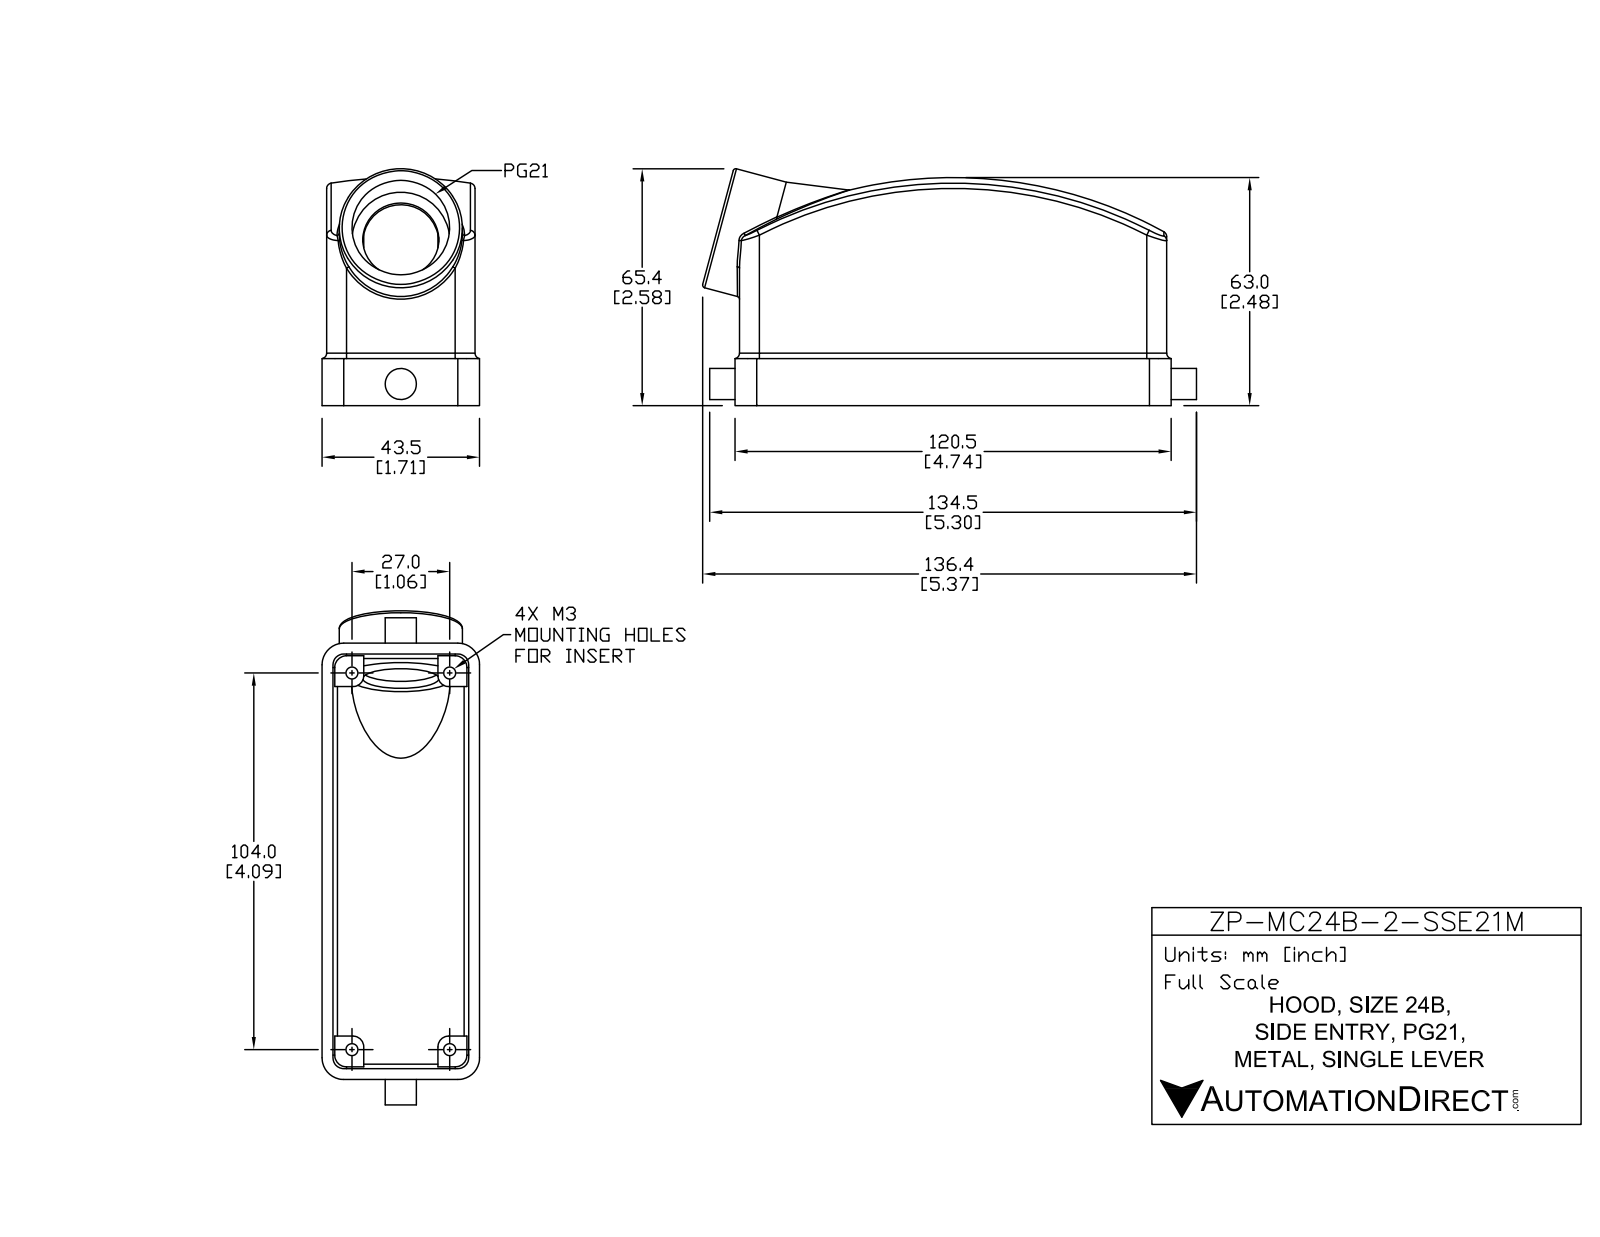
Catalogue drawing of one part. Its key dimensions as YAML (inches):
part_name: "ZP-MC24B-2-SSE21M"
step_written_by: "SolidWorks 2011 (AUTOMOTIVE_DESIGN)"
units: inches
bodies: {solids: 3, faces: 110, planar: 46, cylindrical: 34, other: 30}
overall_size: [5.372, 2.576, 1.713]
volume: 4.421
surface_area: 70.09
round_holes:
  - {diameter: 0.13, count: 4}
  - {diameter: 0.827, count: 1}
  - {diameter: 1.063, count: 1}
round_bosses_or_shafts:
  - {diameter: 1.339, count: 1}
  - {diameter: 0.339, count: 1}
partial_cylinders:
  - {radius: 0.118, count: 8}
  - {radius: 0.059, count: 4}
  - {radius: 0.177, count: 4}
  - {radius: 0.217, count: 4}
  - {radius: 0.236, count: 4}
  - {radius: 0.669, count: 1}
face_to_face_distances: [0.118, 1.496, 0.049, 1.545, 1.614, 1.378, 0.167, 0.069, 1.663, 1.594]
hole_center_spacings: [1.063, 4.094, 4.23]
